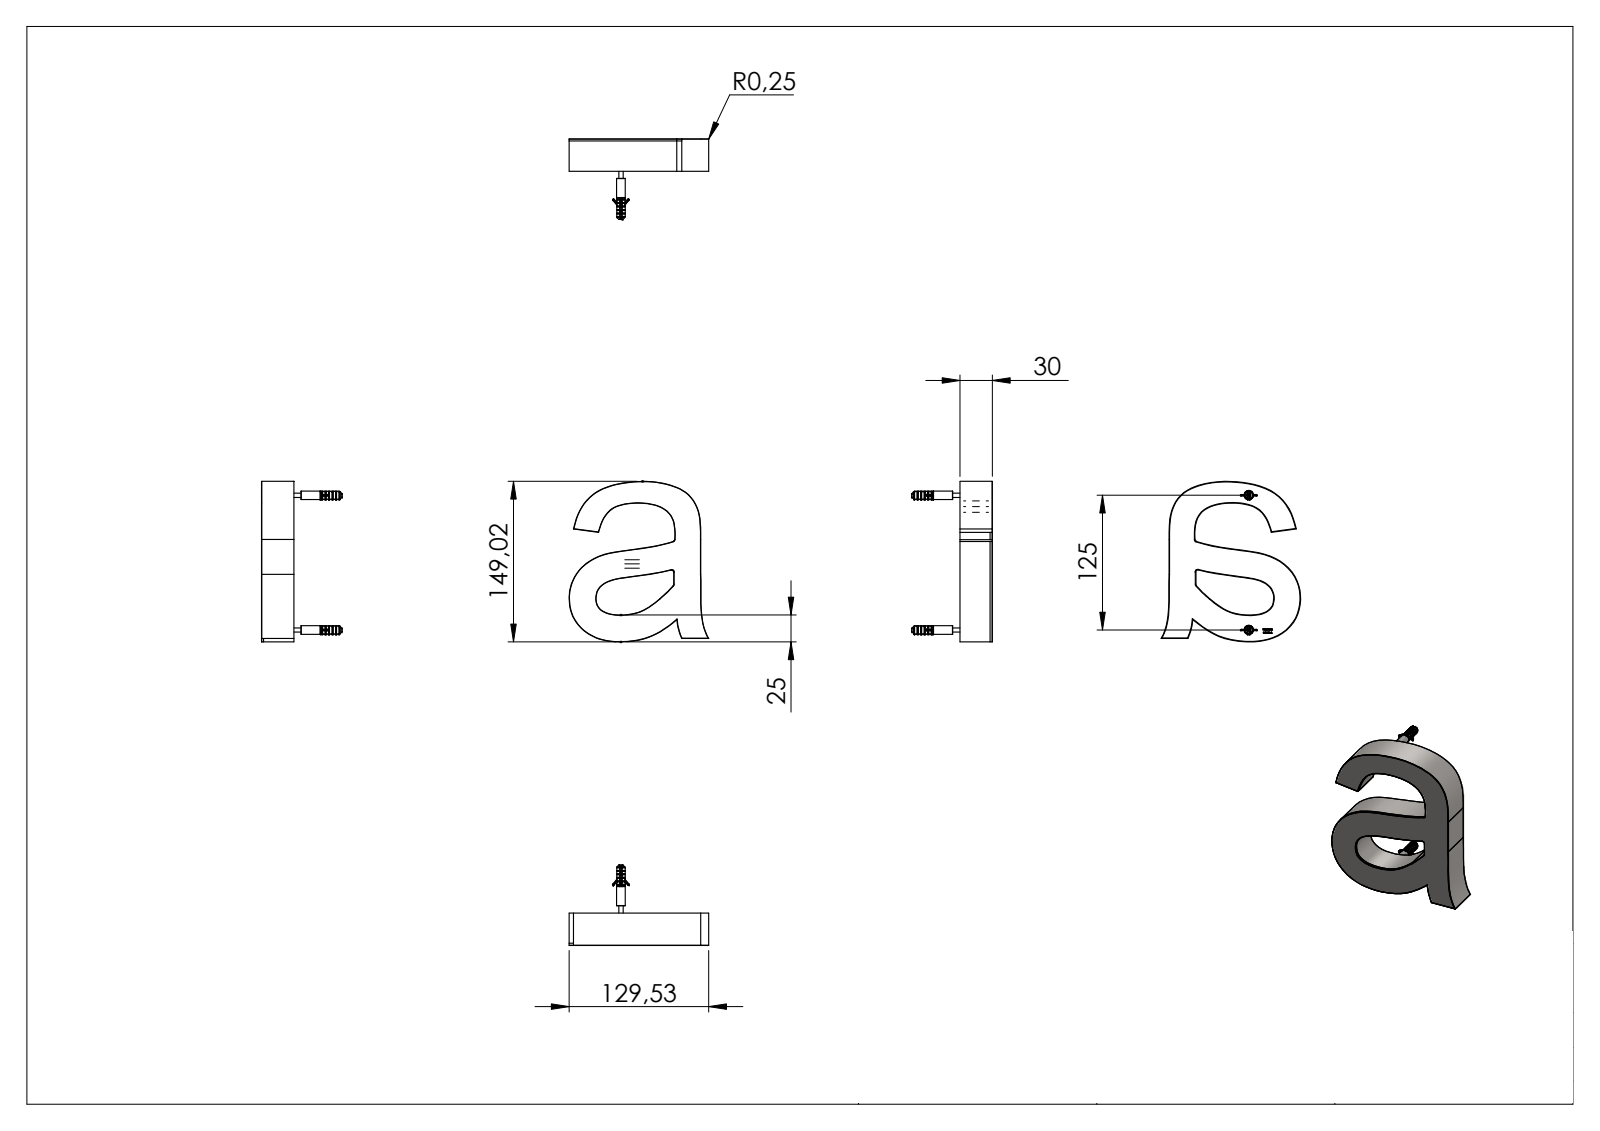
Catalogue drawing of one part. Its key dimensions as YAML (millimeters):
part_name: "042-HN-A; 042-HN-X Teil3_042-HN-X Teil3; 042-HN-X Teil1_042-HN-A Teil1; 042-HN-X Teil2_042-HN-X Teil2"
step_written_by: "SolidWorks 2015 (CONFIG_CONTROL_DESIGN)"
units: millimeters
bodies: {solids: 5, faces: 1149, planar: 260, cylindrical: 308, other: 581}
overall_size: [152.73, 149.03, 129.53]
volume: 38519
surface_area: 77278
round_holes:
  - {diameter: 4.2, count: 2}
round_bosses_or_shafts:
  - {diameter: 1, count: 4}
  - {diameter: 8.5, count: 2}
  - {diameter: 8, count: 2}
  - {diameter: 7.8, count: 2}
  - {diameter: 7, count: 2}
  - {diameter: 6.7, count: 2}
  - {diameter: 5, count: 2}
  - {diameter: 4, count: 2}
partial_cylinders:
  - {radius: 0.5, count: 40}
  - {radius: 0.2, count: 34}
  - {radius: 0.25, count: 4}
  - {radius: 2, count: 3}
  - {radius: 2.5, count: 3}
  - {radius: 123.98, count: 1}
  - {radius: 124.48, count: 1}
face_to_face_distances: [2, 0.5, 24.5, 28, 30, 25, 24, 1.5, 48.38, 48.88]
hole_center_spacings: [125]
